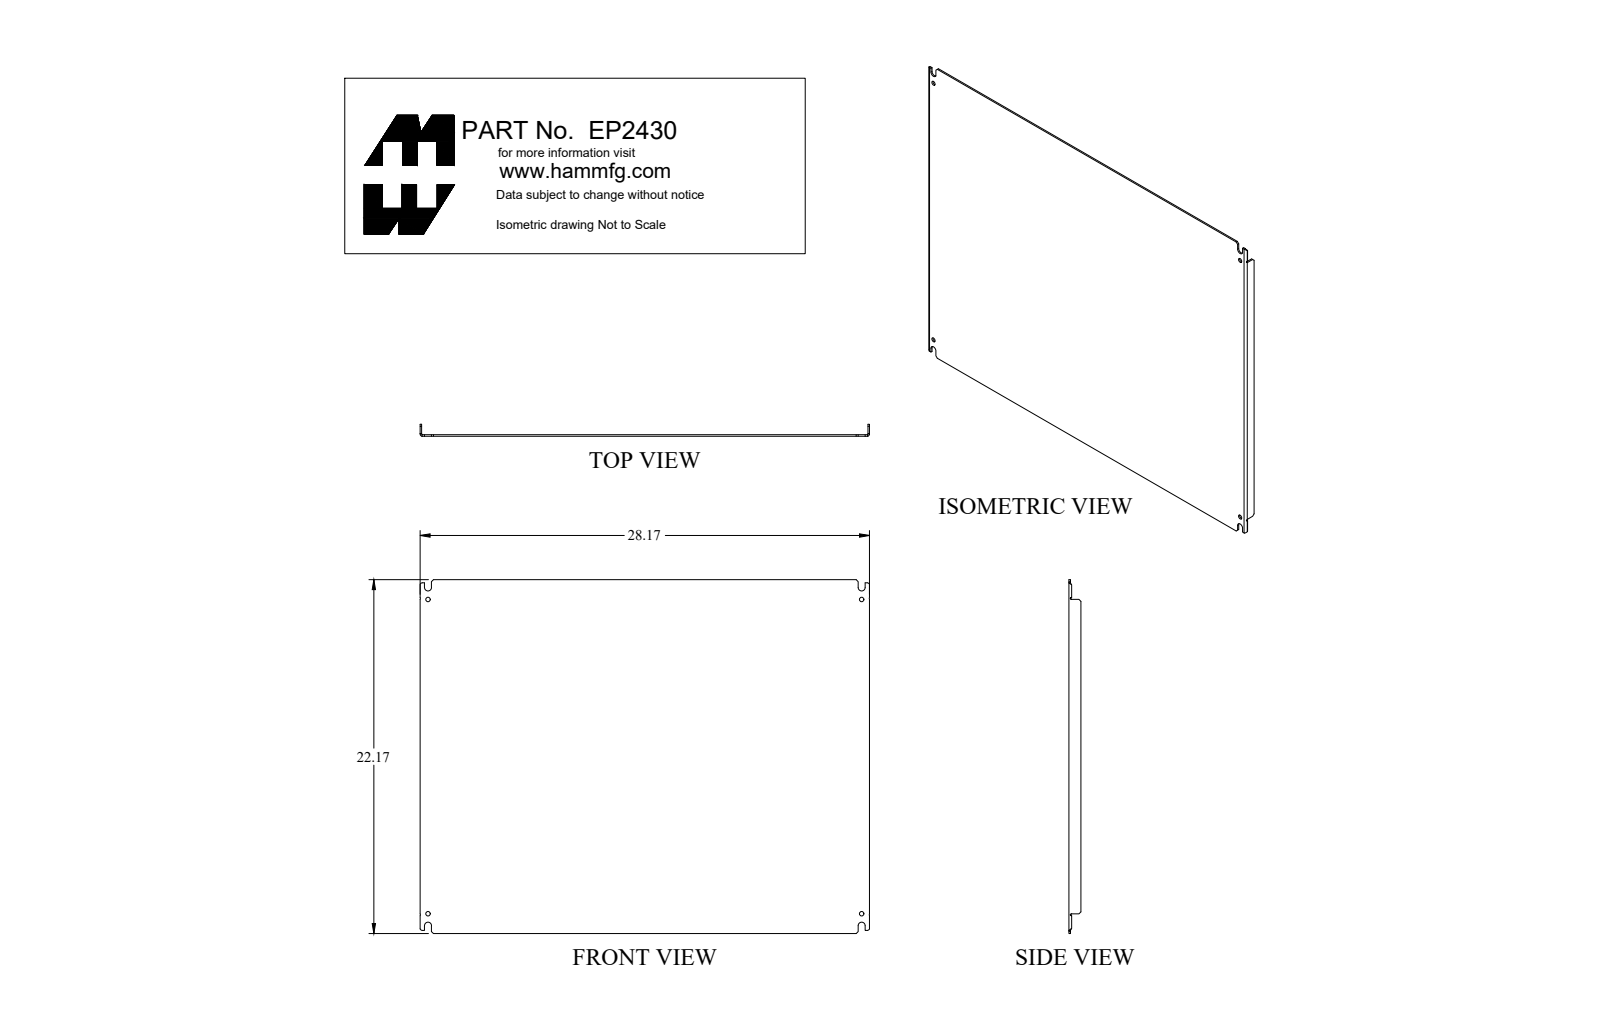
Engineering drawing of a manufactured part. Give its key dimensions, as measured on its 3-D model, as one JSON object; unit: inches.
{"part_name": "EP2430", "step_written_by": "SolidWorks 2018 (AUTOMOTIVE_DESIGN)", "units": "inches", "bodies": {"solids": 1, "faces": 84, "planar": 50, "cylindrical": 26, "other": 8}, "overall_size": [28.17, 22.17, 0.75], "volume_in3": 61.48, "surface_area_in2": 1305, "round_holes": [[0.281, 4]], "partial_cylinders_radius": [[0.219, 4], [0.048, 2], [0.062, 2], [0.143, 2]], "face_to_face_distances": [0.095, 28.075, 27.98, 28.17, 0.75, 0.655, 22.17, 0.171, 0.076, 0.579], "hole_center_spacings": [19.688, 27.188, 33.568]}
